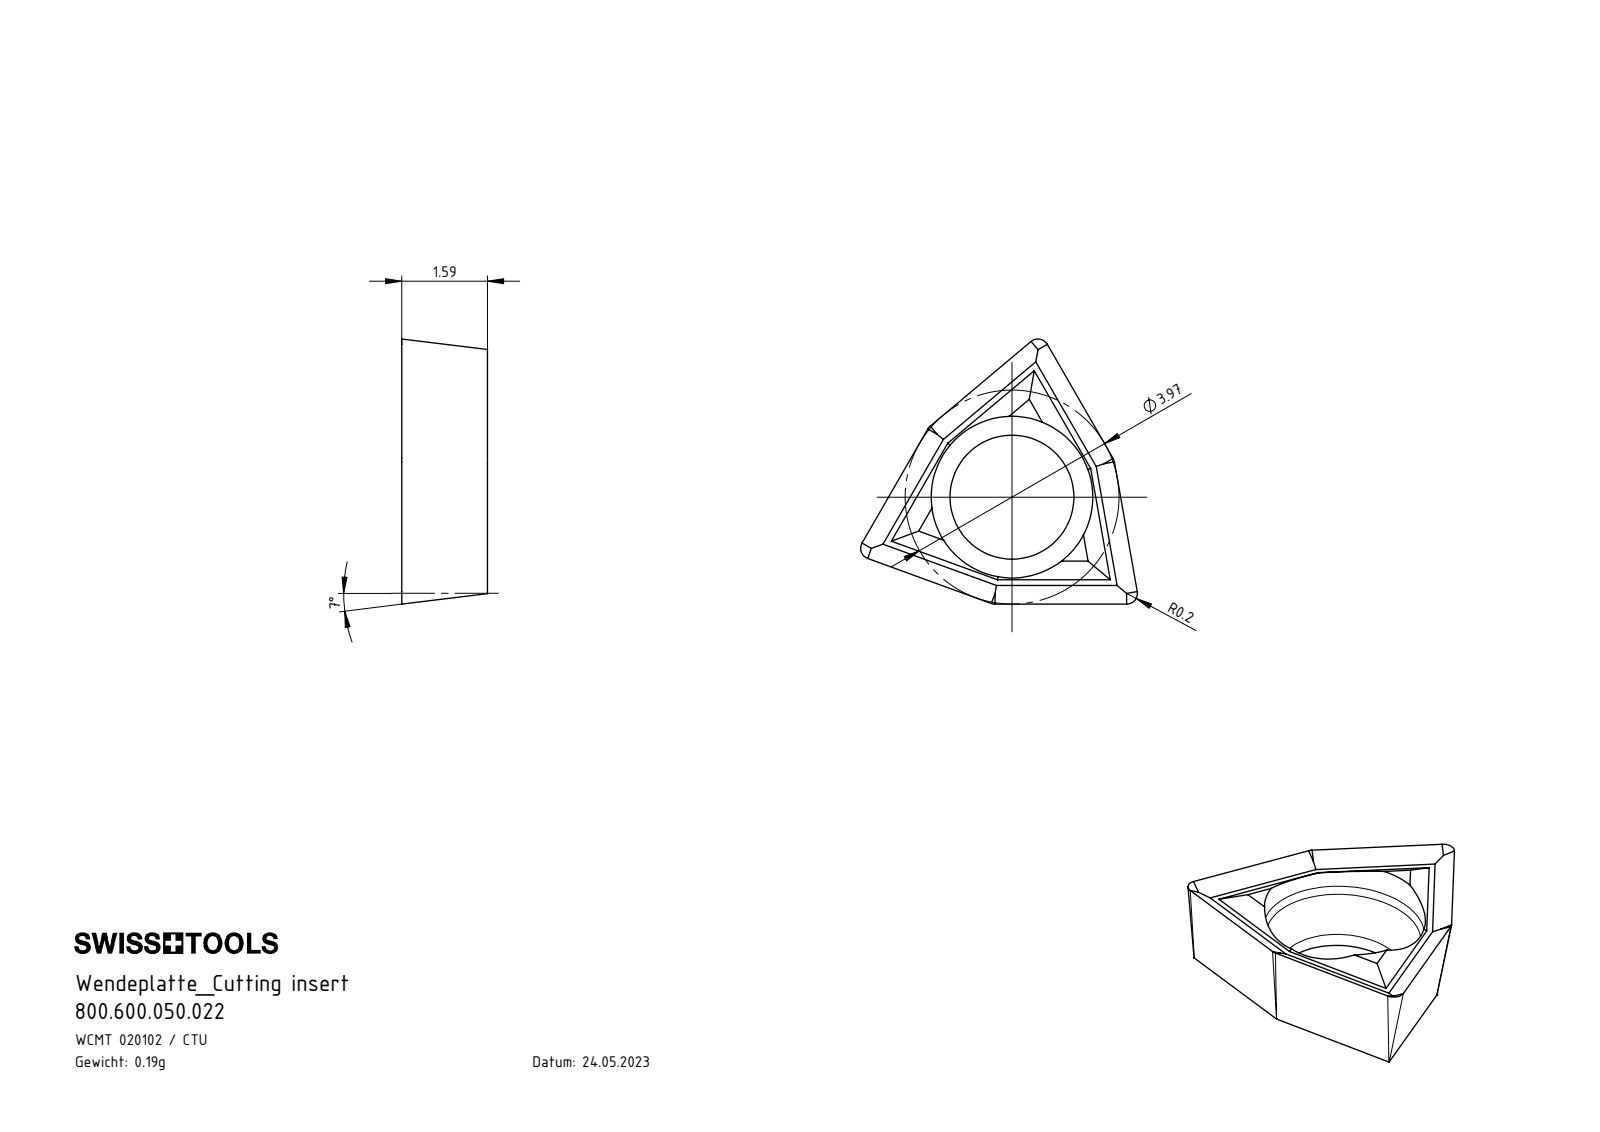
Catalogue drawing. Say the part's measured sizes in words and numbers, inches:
The part is named "800.600.050.022". Its 3-D file was written by "SolidWorks 2017 (AUTOMOTIVE_DESIGN)". It is 1 solid with 43 faces: 23 planar, 4 cylindrical and 16 other. Overall it measures 0.202 by 0.194 by 0.063 inches. Its volume is 0.001 cubic inches and its surface area 0.088 square inches. Round holes: 1 of diameter 0.091, 1 of diameter 0.118. The main face-to-face distances are 0.055, 0.063.
